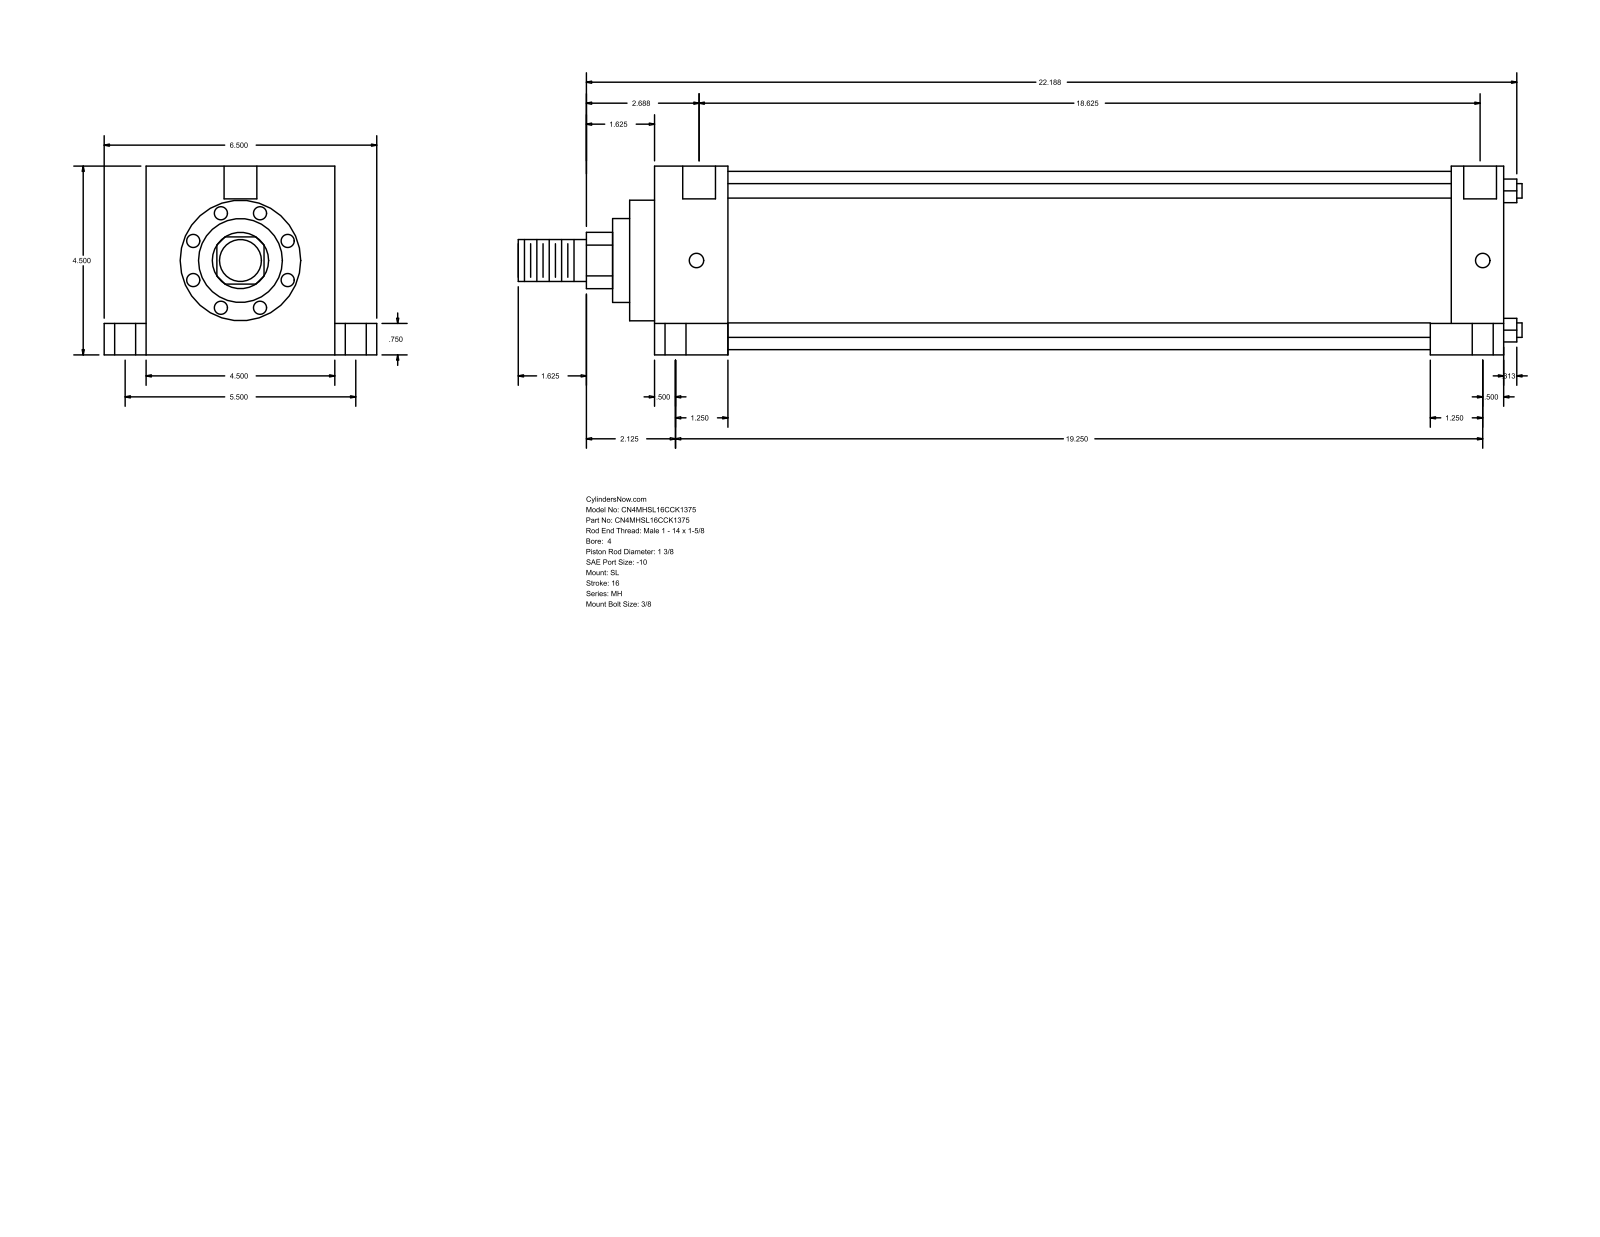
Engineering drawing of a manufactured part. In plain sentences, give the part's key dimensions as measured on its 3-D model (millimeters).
The part is named "MH_SL__0400_1.375". Its 3-D file was written by "GSSL Pune (CONFIG_CONTROL_DESIGN)". It is 0 solids with 110 faces: 77 planar, 33 cylindrical and 0 other. Overall it measures 608.01 by 165.1 by 114.3 millimeters. Round holes: 4 of diameter 8.73, 4 of diameter 12.7, 4 of diameter 19.05, 2 of diameter 19.84. Round bosses or shafts: 4 of diameter 8.76, 1 of diameter 107.95, 1 of diameter 73.03, 1 of diameter 50.8, 1 of diameter 34.92, 1 of diameter 25.4. Partial cylindrical surfaces (rounded edges, fillets, slot ends): 1 of radius 17.06. The main face-to-face distances are 114.3, 514.35, 44.45, 469.9, 482.61, 438.16, 31.74, 25.4, 139.7, 19.05. The hole center spacings are 69.85, 69.87, 70.99, 71.29, 139.7, 476.25, 479.77, 481.35.
